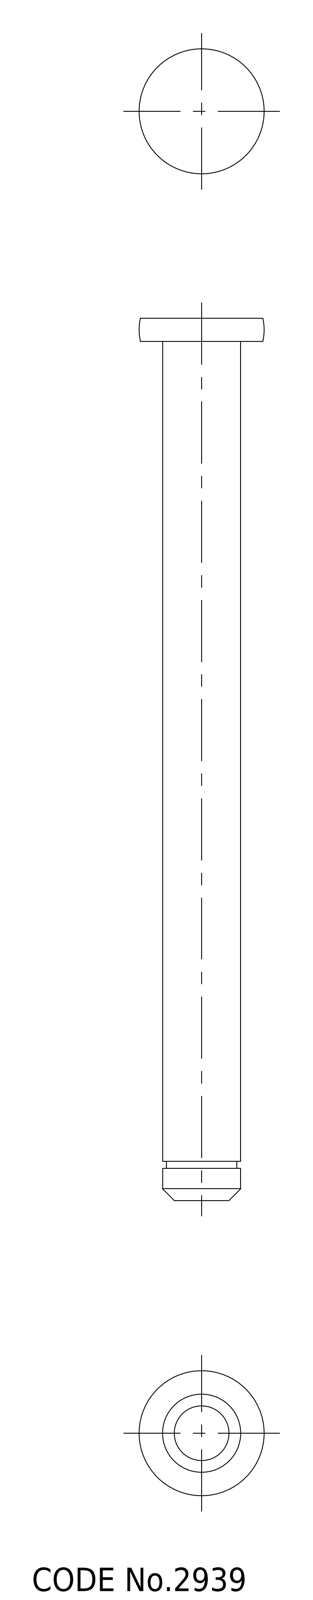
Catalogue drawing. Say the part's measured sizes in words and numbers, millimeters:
The part is named "shaft; TH_121_10_110". Its 3-D file was written by "SolidWorks 2015 (AUTOMOTIVE_DESIGN)". It is 1 solid with 15 faces: 5 planar, 6 cylindrical and 4 other. Overall it measures 113 by 16 by 16 millimeters. Its volume is 9 189 cubic millimeters and its surface area 3 988 square millimeters. Round bosses or shafts: 1 of diameter 10, 1 of diameter 9. The main face-to-face distances are 3, 110, 113, 4.1, 5, 0.9, 105.9, 108.9, 105, 108.
